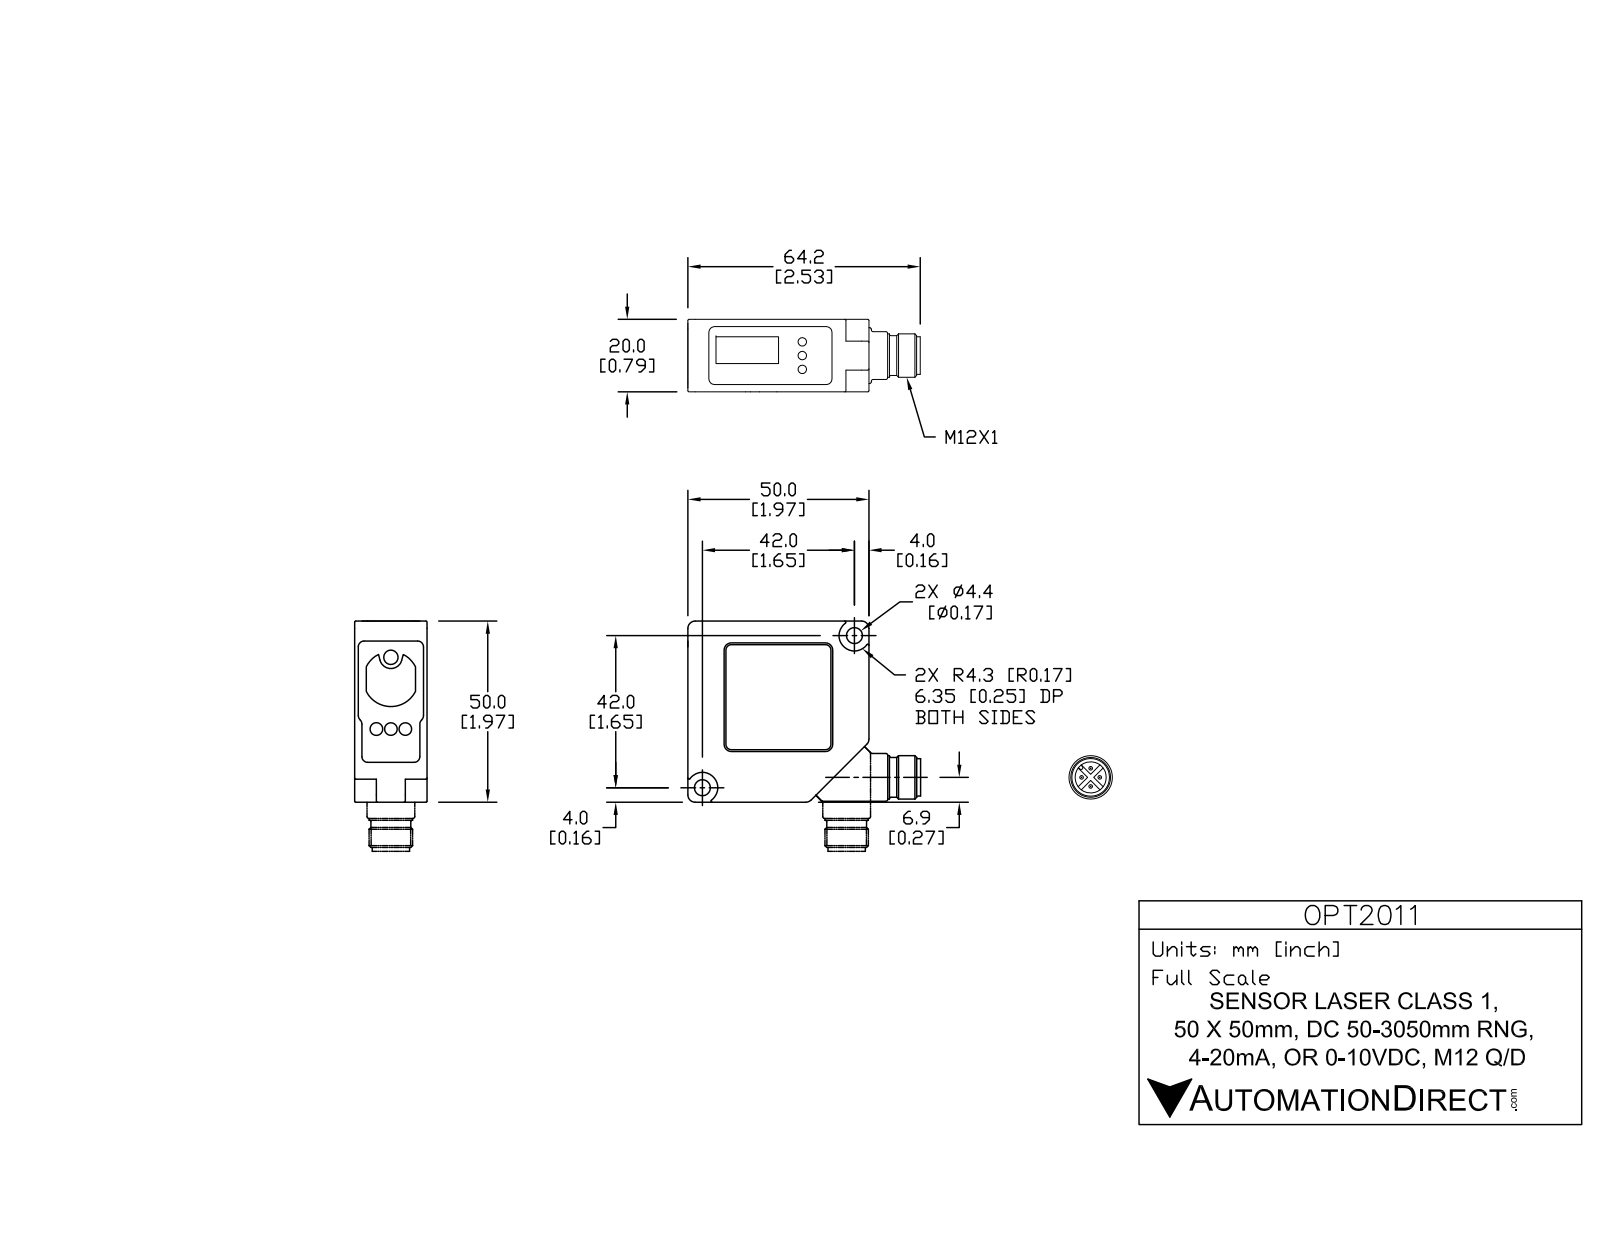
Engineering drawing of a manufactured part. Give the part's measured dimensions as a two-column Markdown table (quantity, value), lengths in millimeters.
| quantity | value |
| --- | --- |
| part name | OPT2011 |
| STEP written by | SolidWorks 2013 (AUTOMOTIVE_DESIGN) |
| units | millimeters |
| bodies | 13 solids, 344 faces (136 planar, 185 cylindrical, 23 other) |
| overall size | 64.43 × 50 × 20 |
| volume | 47 209 mm³ |
| surface area | 17 842 mm² |
| round holes (diameter × count) | 3.5 × 3, 3.47 × 2, 4.4 × 2, 2.29 × 1, 3.47 × 1, 3.95 × 1, 8.45 × 1, 15.2 × 1 |
| round bosses / shafts (diameter × count) | 1 × 4, 18 × 1, 13.5 × 1, 12 × 1, 11 × 1, 10.3 × 1 |
| partial cylindrical surfaces (radius × count) | 0.3 × 14, 1.6 × 12, 2 × 10, 0.2 × 4, 1 × 4, 0.75 × 2, 0.95 × 2, 3.35 × 2 |
| main face-to-face distances | 1, 20, 19.8, 50, 3, 1.5, 0.5, 48.5, 4.5, 4 |
| hole center spacings | 4, 6.33, 8, 14.03, 14.37, 20.2, 4.9, 6 |
